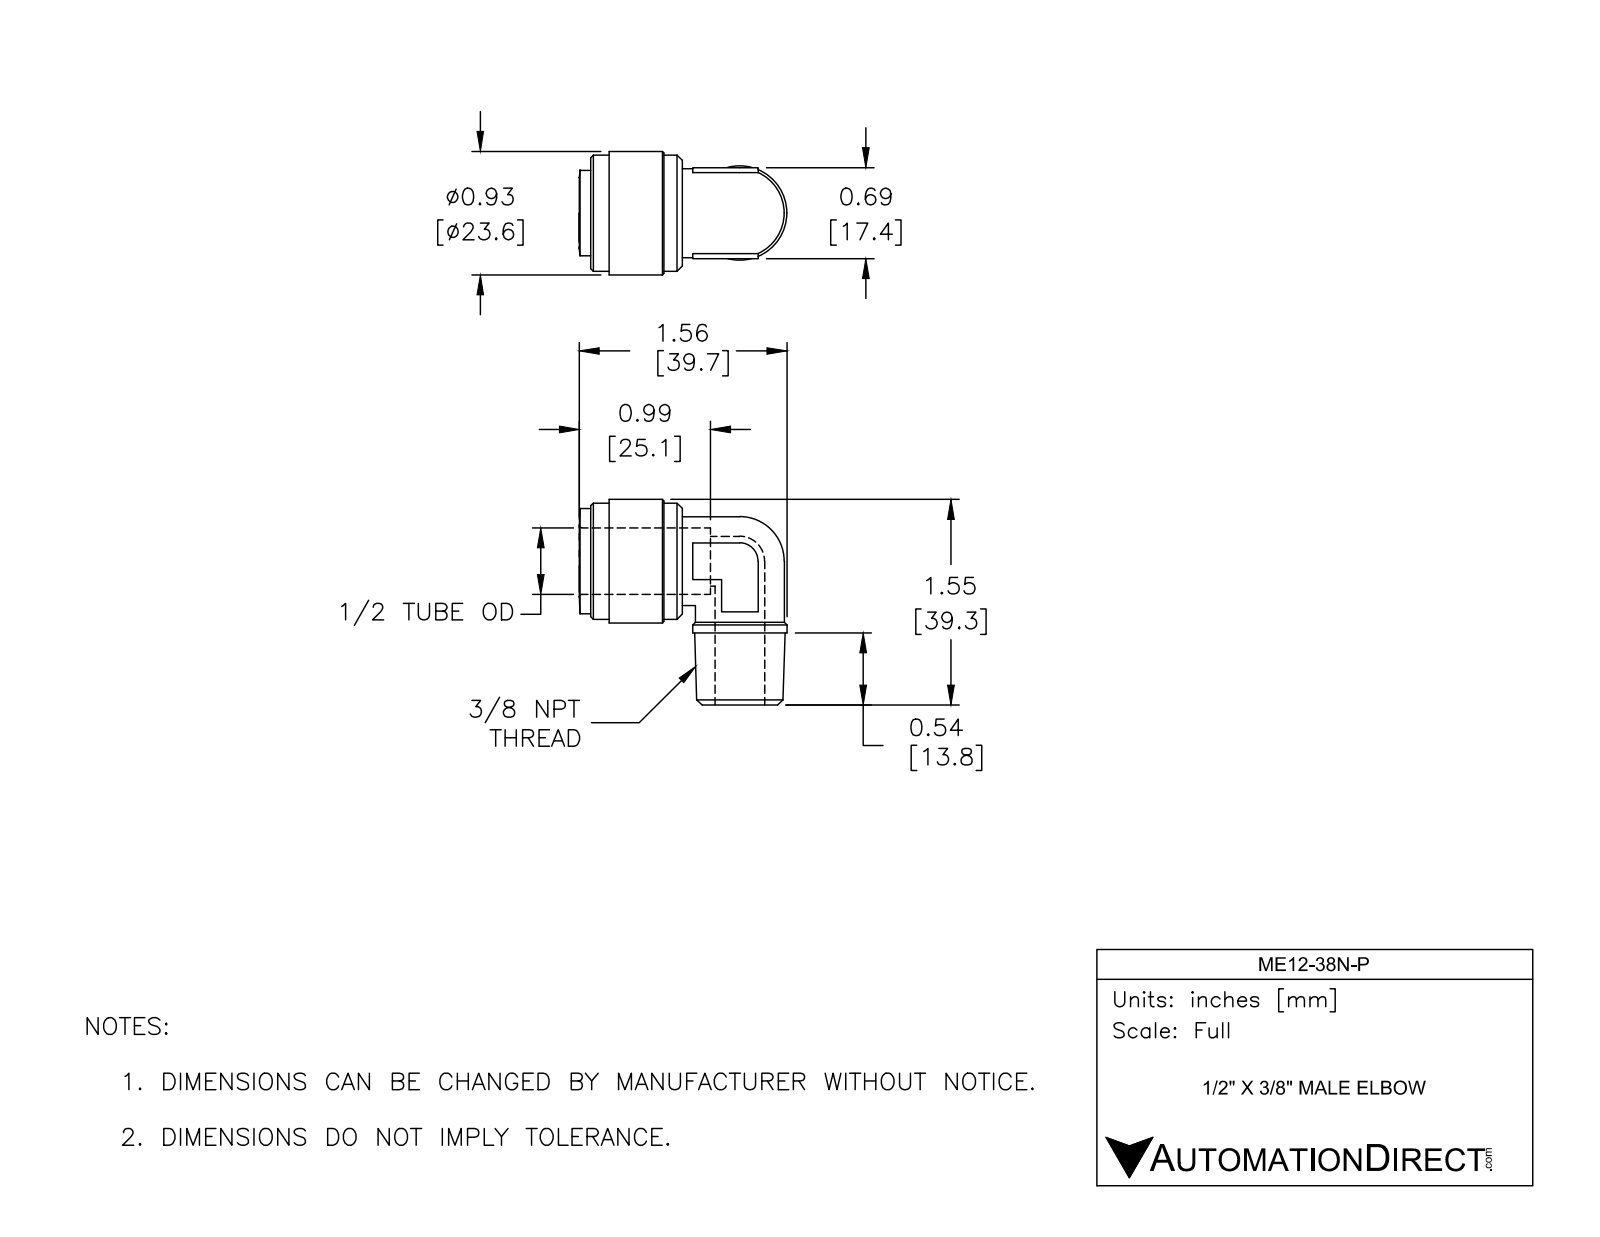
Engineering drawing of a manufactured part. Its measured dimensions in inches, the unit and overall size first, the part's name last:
Units: inches
Overall size (bounding box): 1.563 × 1.547 × 0.929
Round holes (diameter × count): ⌀0.374 ×2, ⌀0.5 ×1
Round bosses / shafts (diameter × count): ⌀0.669 ×2, ⌀0.929 ×1, ⌀0.874 ×1, ⌀0.709 ×1
Partial cylindrical surfaces — rounded edges, fillets, slot ends (radius × count): R0.138 ×1
Main face-to-face distances: 0.685, 0.689, 0.138, 0.551, 0.902, 0.213, 0.764, 0.413, 0.35, 0.276
Volume: 0.669 in³ · Surface area: 9.385 in²
Bodies: 1 solid, 63 faces (21 planar, 20 cylindrical, 22 other)
Part name (STEP PRODUCT): ME12-38N-P
STEP written by: SolidWorks 2017 (AUTOMOTIVE_DESIGN)
